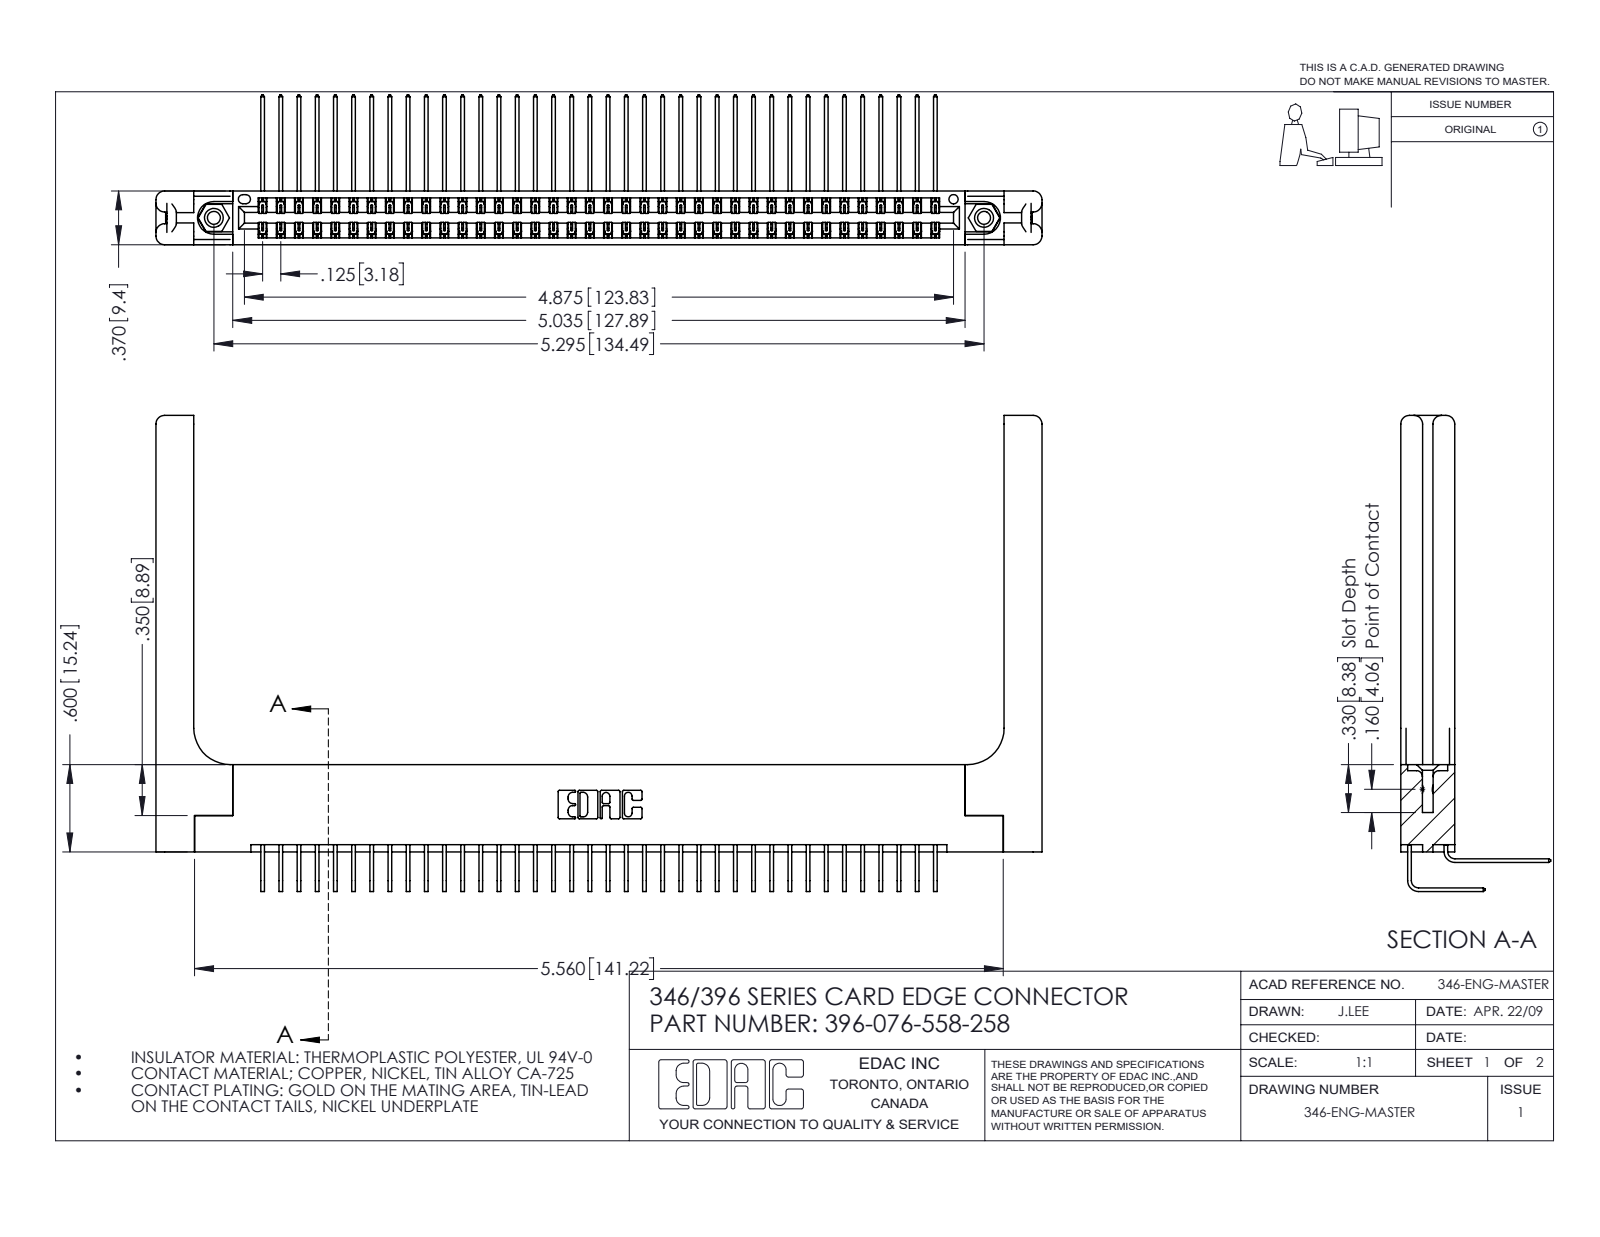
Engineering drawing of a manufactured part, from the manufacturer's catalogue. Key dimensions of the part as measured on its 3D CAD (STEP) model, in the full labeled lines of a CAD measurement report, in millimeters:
Part name (STEP PRODUCT): 346-220-058_345-220-058; 345-250-001_345-250-001-102; 345-292-001_558 Tail - 2; 396-076-558-258 (+2 more)
STEP written by: SolidWorks 2016 (CONFIG_CONTROL_DESIGN)
Units: millimetres
Bodies: 81 solids, 4482 faces (3036 planar, 1386 cylindrical, 60 other)
Overall size (bounding box): 154.7 × 83.1 × 26.2
Volume: 22 990 mm³ · Surface area: 28 310 mm²
Round holes (diameter × count): ⌀2.3 ×2, ⌀3.2 ×2, ⌀4 ×2, ⌀1.6 ×1
Round bosses / shafts (diameter × count): ⌀3.9 ×2
Partial cylindrical surfaces — rounded edges, fillets, slot ends (radius × count): R0.2 ×114, R0.3 ×22, R1.5 ×16, R0.2 ×6, R0.8 ×6, R0.7 ×3, R0.4 ×2, R0.6 ×2
Main face-to-face distances: 8.2, 1.2, 9.4, 1.8, 0.6, 7.6, 3.8, 3.8, 6.4, 7
Hole centre spacings: 6.2, 129.2, 134.5
